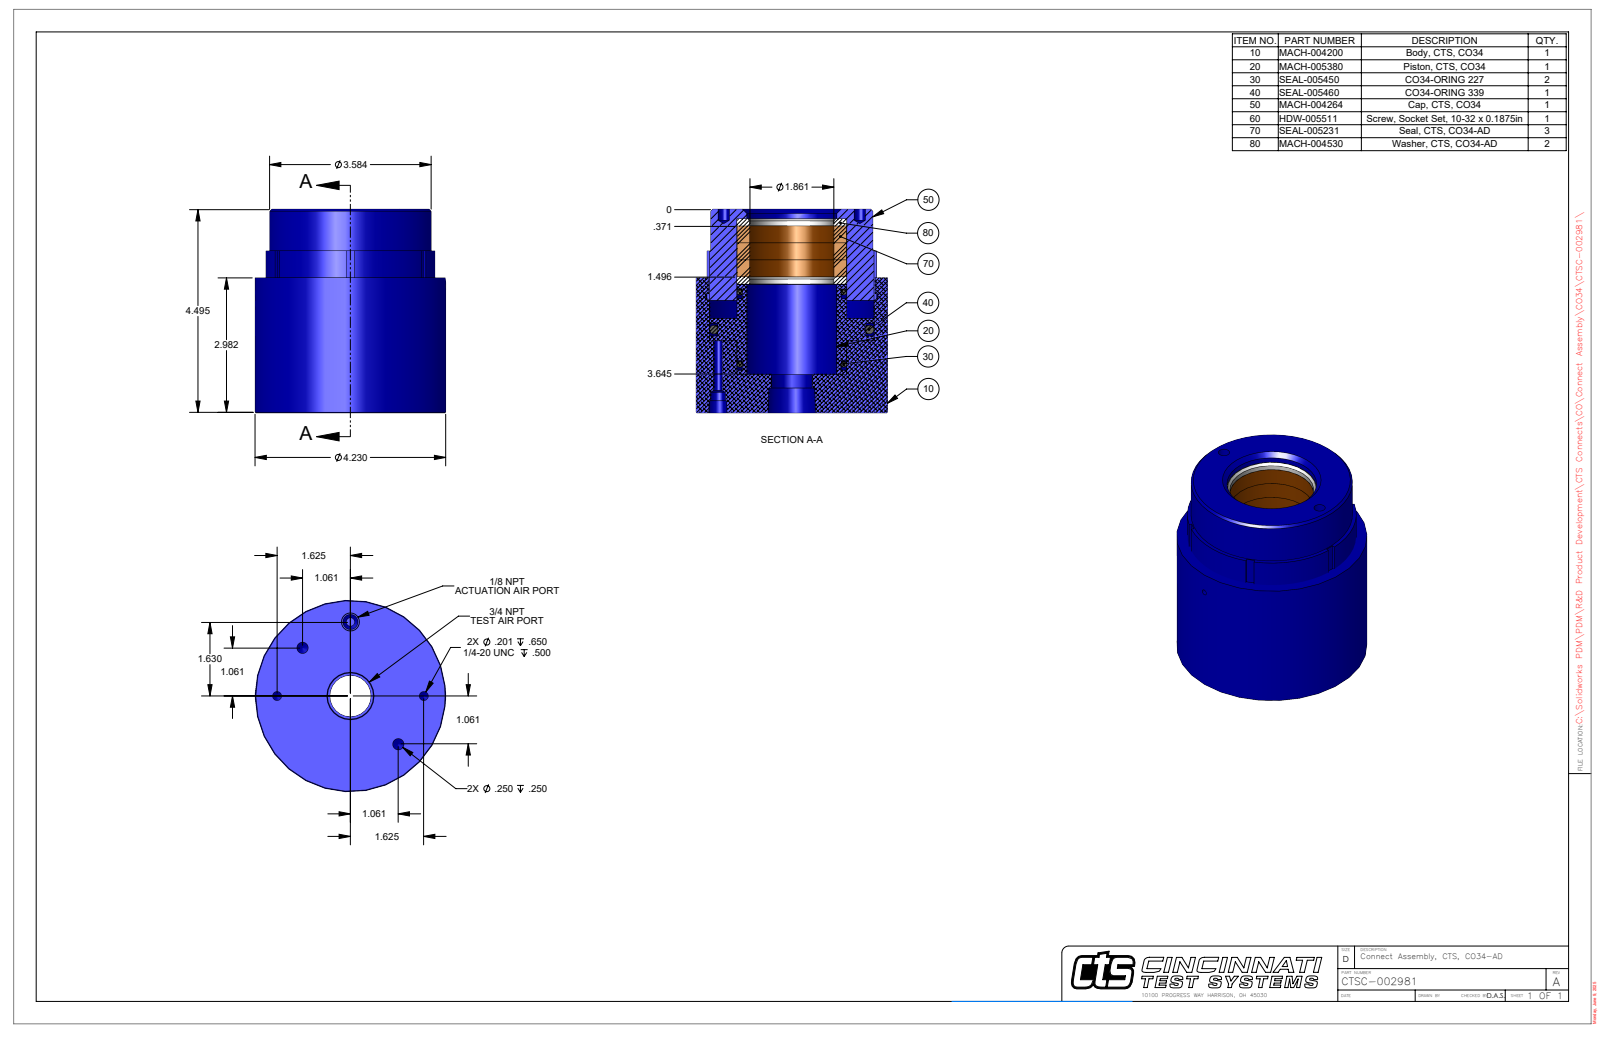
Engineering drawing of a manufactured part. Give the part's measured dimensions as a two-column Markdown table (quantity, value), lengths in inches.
| quantity | value |
| --- | --- |
| part name | CTSC-002981 |
| STEP written by | SolidWorks 2023 (AUTOMOTIVE_DESIGN) |
| units | inches |
| bodies | 2 solids, 135 faces (49 planar, 60 cylindrical, 26 other) |
| overall size | 4.495 × 4.231 × 4.23 |
| volume | 46.12 in³ |
| surface area | 120.9 in² |
| round holes (diameter × count) | 0.25 × 4, 0.201 × 2, 0.125 × 1, 0.159 × 1, 0.187 × 1, 0.332 × 1, 0.906 × 1, 1.861 × 1, 1.863 × 1, 1.904 × 1, 1.987 × 1, 1.988 × 1 |
| round bosses / shafts (diameter × count) | 4.23 × 1, 3.75 × 1, 3.584 × 1, 2.416 × 1 |
| partial cylindrical surfaces (radius × count) | 1.844 × 1, 2.102 × 1 |
| main face-to-face distances | 4.495, 1.298, 4.28, 0.215, 2.982, 1.513, 0.156, 0.85, 2.132, 3.43 |
| hole center spacings | 1.5, 2.211, 1.148, 1.201, 1.625, 2.302, 2.772, 2.887 |
